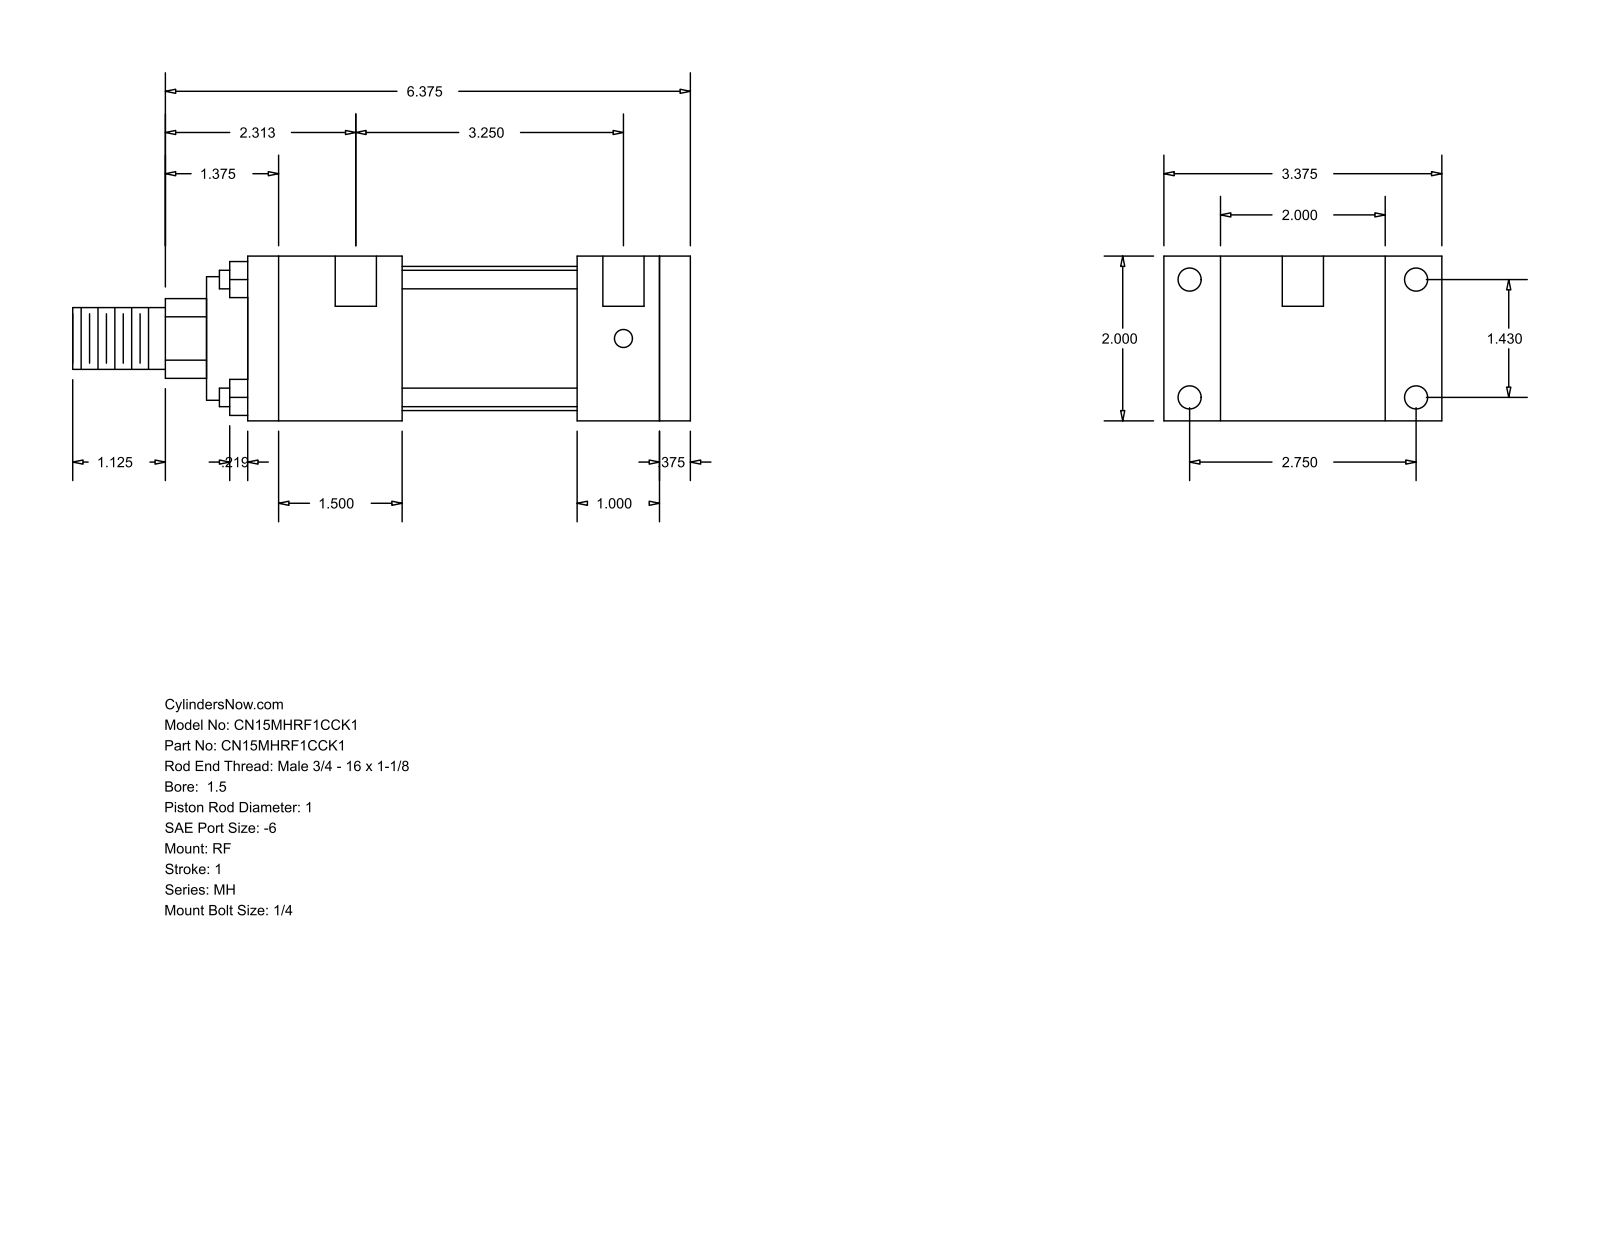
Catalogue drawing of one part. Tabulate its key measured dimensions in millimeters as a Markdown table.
| quantity | value |
| --- | --- |
| part name | MH_RF__0150_1 |
| STEP written by | GSSL Pune (CONFIG_CONTROL_DESIGN) |
| units | millimeters |
| bodies | 0 solids, 92 faces (64 planar, 28 cylindrical, 0 other) |
| overall size | 190.5 × 85.72 × 50.8 |
| round holes (diameter × count) | 5.56 × 4, 7.14 × 4, 12.7 × 2 |
| round bosses / shafts (diameter × count) | 5.71 × 4, 44.45 × 1, 38.1 × 1, 25.4 × 1, 19.05 × 1 |
| partial cylindrical surfaces (radius × count) | 12.29 × 1 |
| main face-to-face distances | 50.8, 9.53, 101.6, 53.97, 127, 25.4, 136.53, 17.46, 68.26, 34.93 |
| hole center spacings | 36.32, 69.84, 78.72, 85.73, 3.18, 82.55 |
